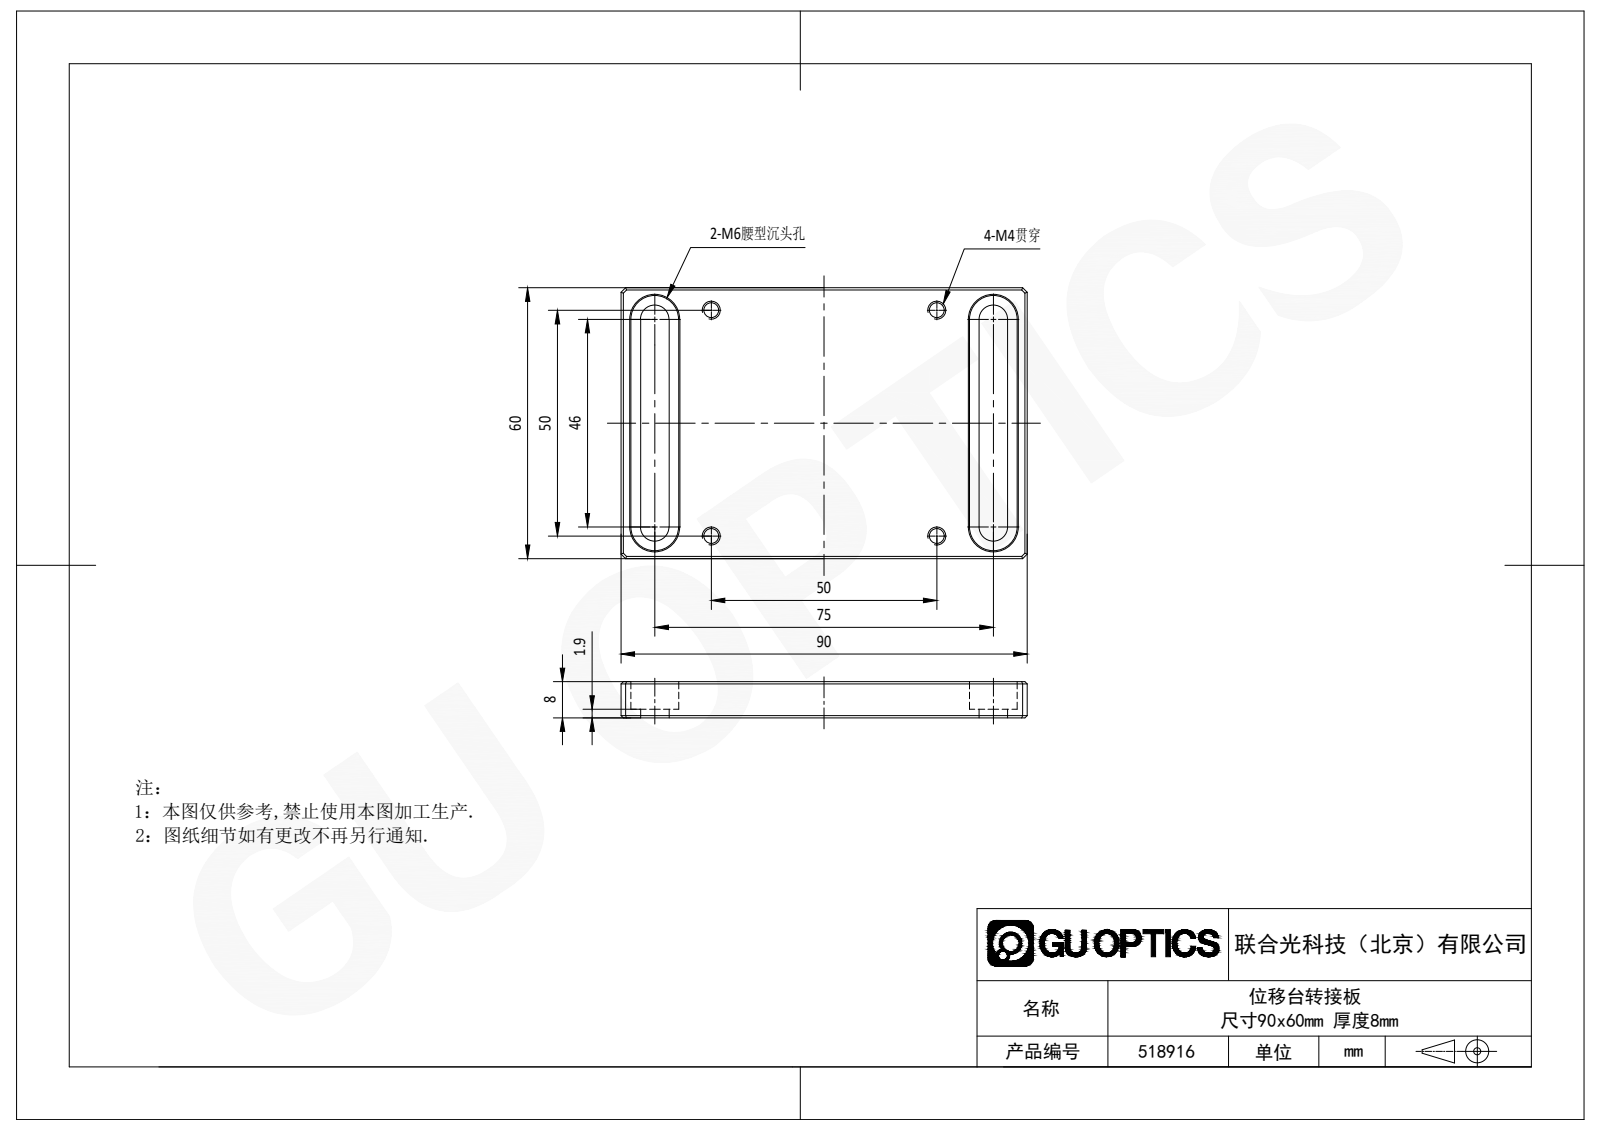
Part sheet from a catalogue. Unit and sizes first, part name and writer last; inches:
Units: inches
Overall size (bounding box): 3.543 × 2.362 × 0.315
Round holes (diameter × count): ⌀0.13 ×4
Partial cylindrical surfaces — rounded edges, fillets, slot ends (radius × count): R0.124 ×4, R0.209 ×4
Main face-to-face distances: 0.315, 2.953, 2.362, 0.087, 0.504, 3.039, 3.457, 0.417, 0.075, 0.24
Hole centre spacings: 1.969, 2.784
Volume: 2.11 in³ · Surface area: 21.53 in²
Bodies: 1 solid, 60 faces (40 planar, 12 cylindrical, 8 other)
STEP written by: SolidWorks 2020 (CONFIG_CONTROL_DESIGN)
